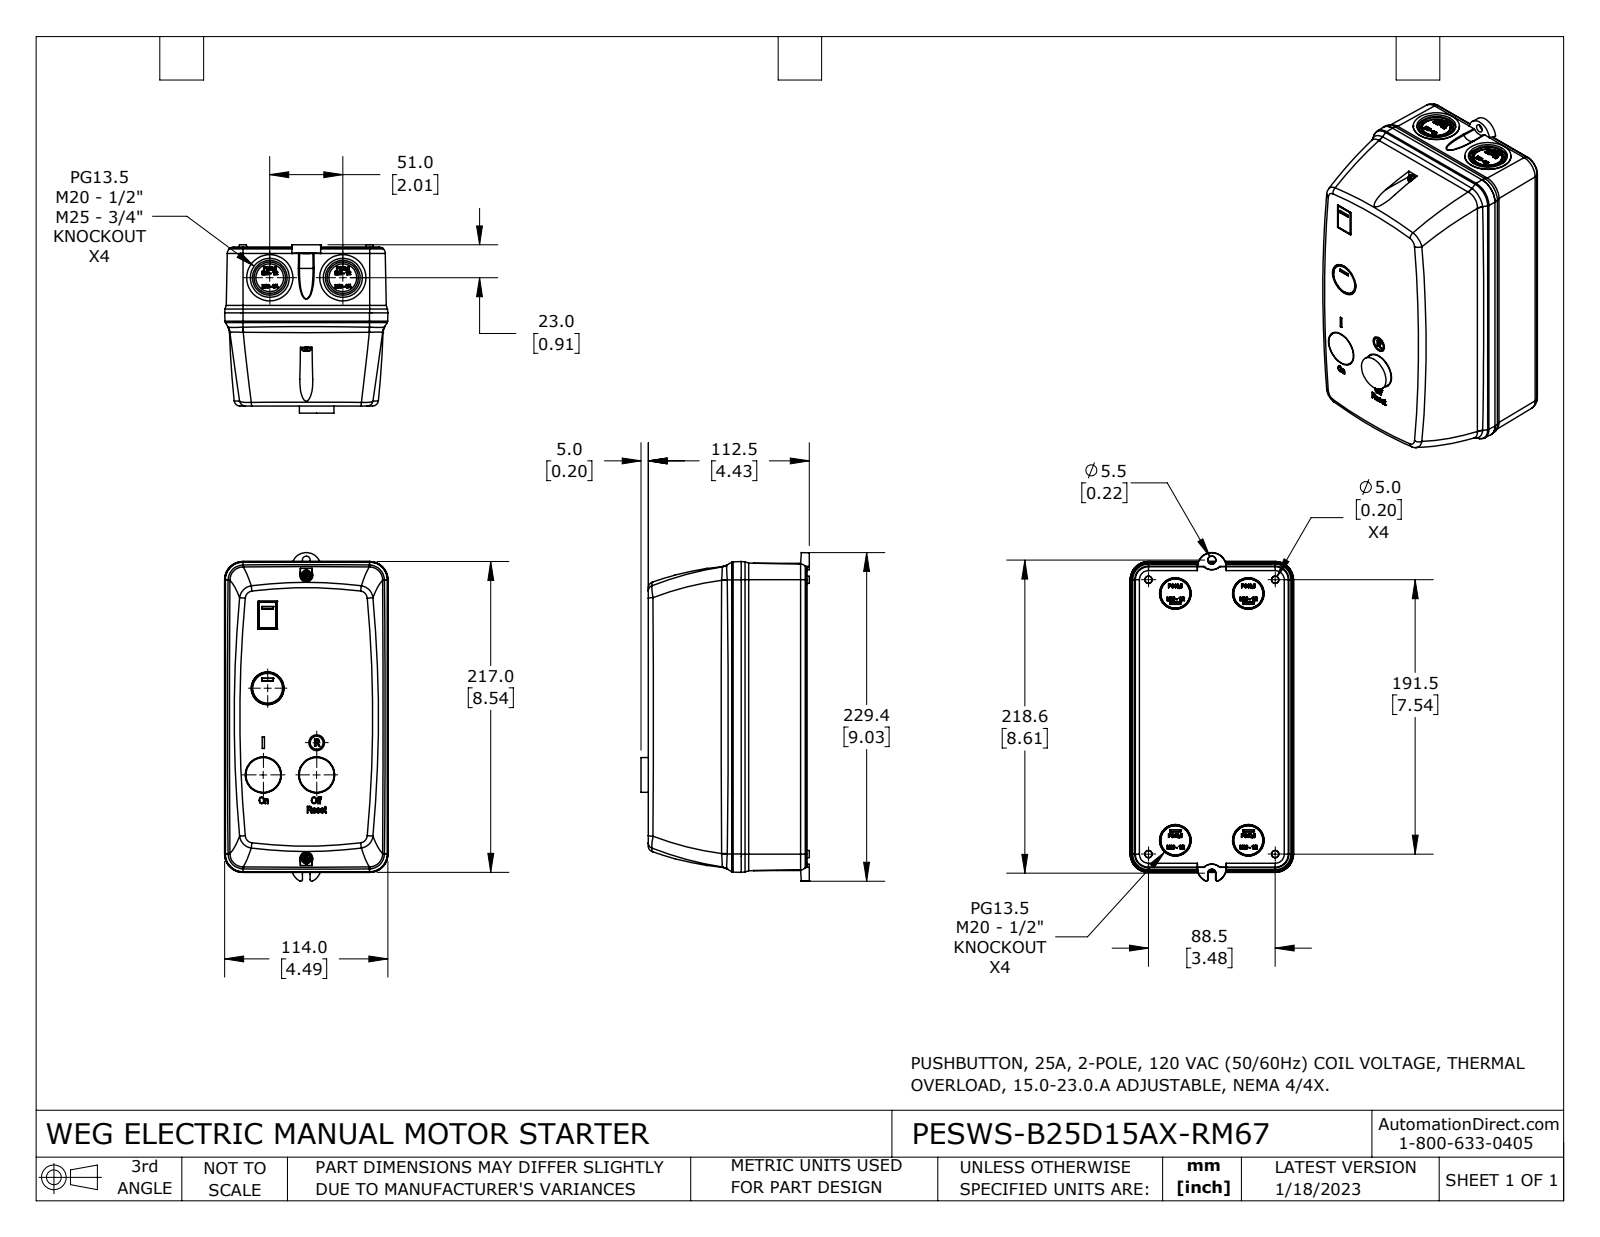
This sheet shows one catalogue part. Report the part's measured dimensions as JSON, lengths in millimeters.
{"part_name": "PESWS-B25D15AX-RM67", "step_written_by": "SolidWorks 2021 (CONFIG_CONTROL_DESIGN)", "units": "millimeters", "bodies": {"solids": 6, "faces": 2195, "planar": 1110, "cylindrical": 92, "other": 993}, "overall_size": [229.44, 117.5, 114.01], "volume_mm3": 2457000, "surface_area_mm2": 166196, "round_holes": [[4.4, 2], [21.91, 2], [27.24, 2], [5.5, 1], [11, 1]], "round_bosses_or_shafts": [[32.26, 2], [24.25, 2], [24.2, 2], [19.37, 2], [7, 2], [3, 2], [9, 1]], "partial_cylinders_radius": [[2, 4], [4.61, 4], [9.54, 4], [6.54, 2], [7.54, 2], [2.08, 1], [2.17, 1], [2.75, 1]], "face_to_face_distances": [46, 65, 111, 0.5, 110.5, 45.5, 110, 1, 109.5, 64], "hole_center_spacings": [10.5, 51, 81.32, 117.22, 127.71, 198, 208.5]}
